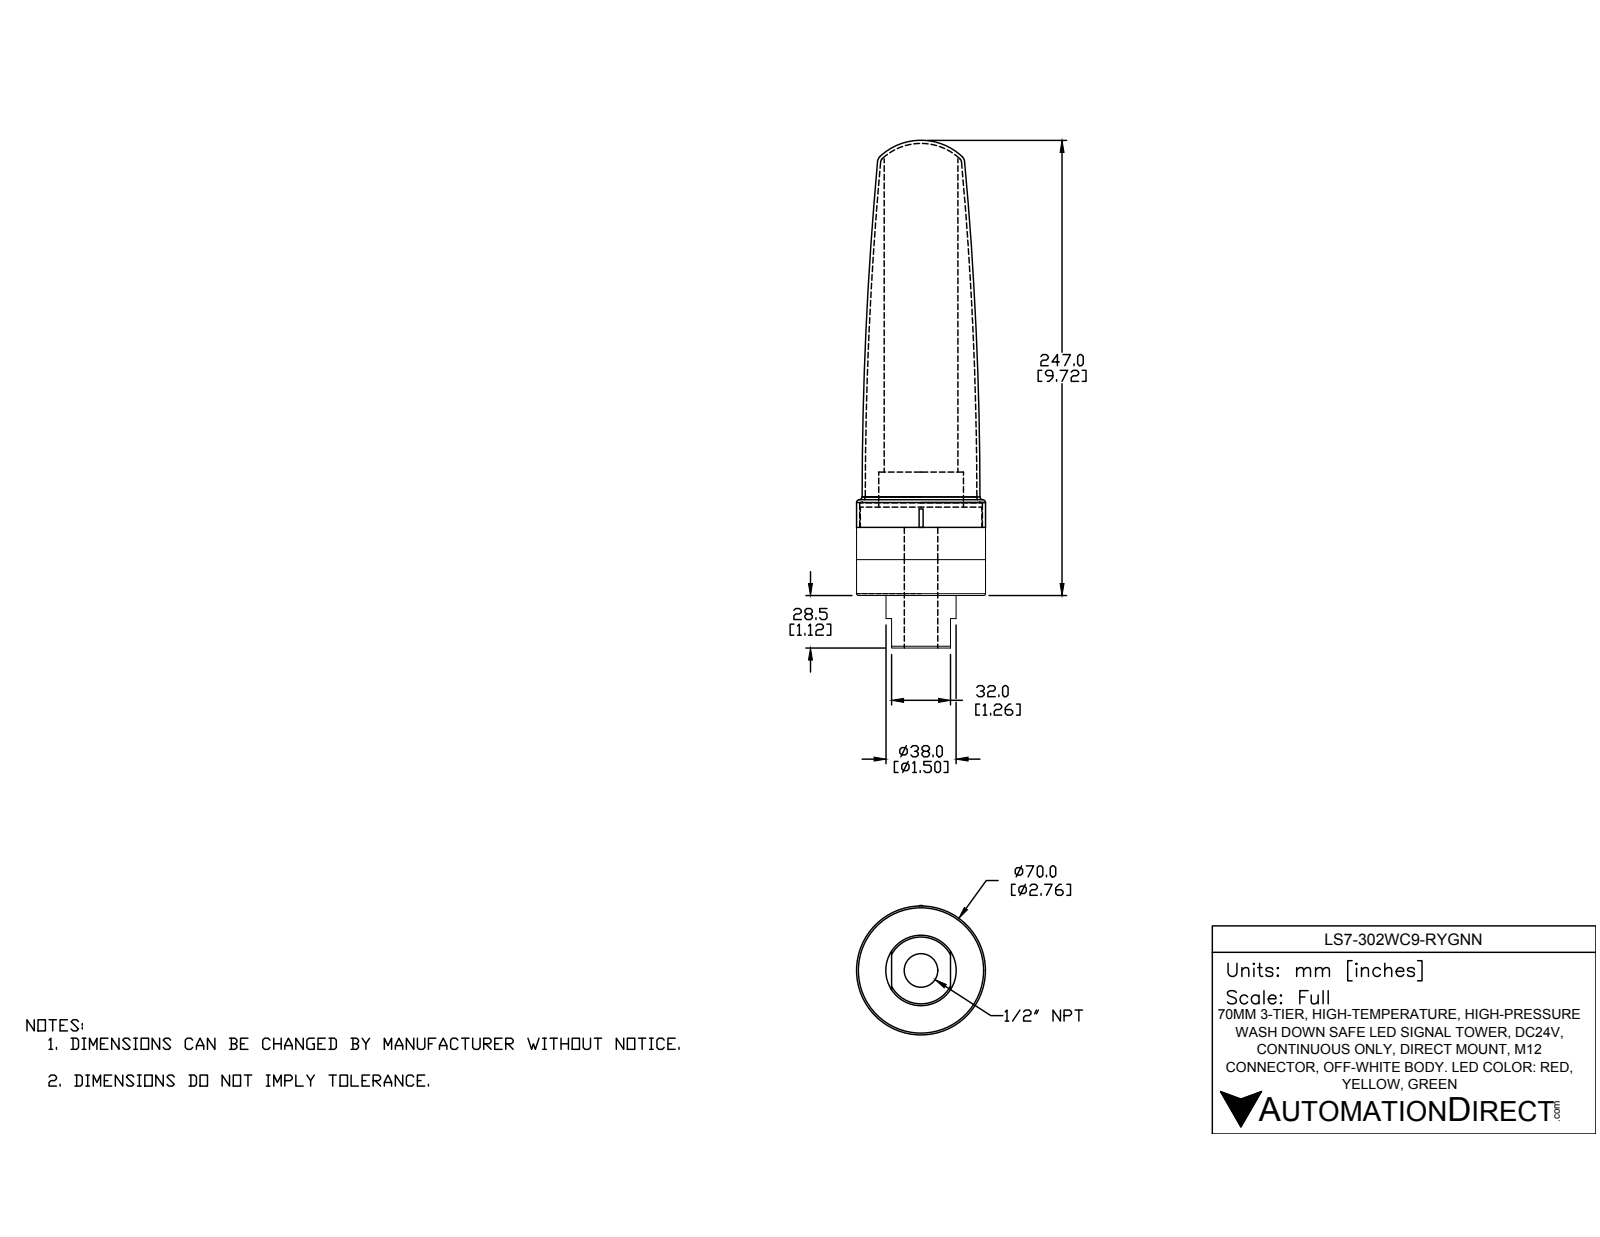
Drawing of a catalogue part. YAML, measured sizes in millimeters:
part_name: "LS7-302WC9-RYGNN"
step_written_by: "SolidWorks 2016 (AUTOMOTIVE_DESIGN)"
units: millimeters
bodies: {solids: 4, faces: 60, planar: 17, cylindrical: 20, other: 23}
overall_size: [275.5, 70.3, 70]
volume: 472008
surface_area: 133775
round_holes:
  - {diameter: 18.2, count: 1}
  - {diameter: 66.6, count: 1}
round_bosses_or_shafts:
  - {diameter: 70, count: 1}
  - {diameter: 46, count: 1}
  - {diameter: 40, count: 1}
  - {diameter: 38, count: 1}
partial_cylinders:
  - {radius: 1, count: 1}
  - {radius: 2, count: 1}
face_to_face_distances: [35.5, 19.5, 55, 37, 17.5, 18, 229.62, 210.12, 192.62, 174.62]
